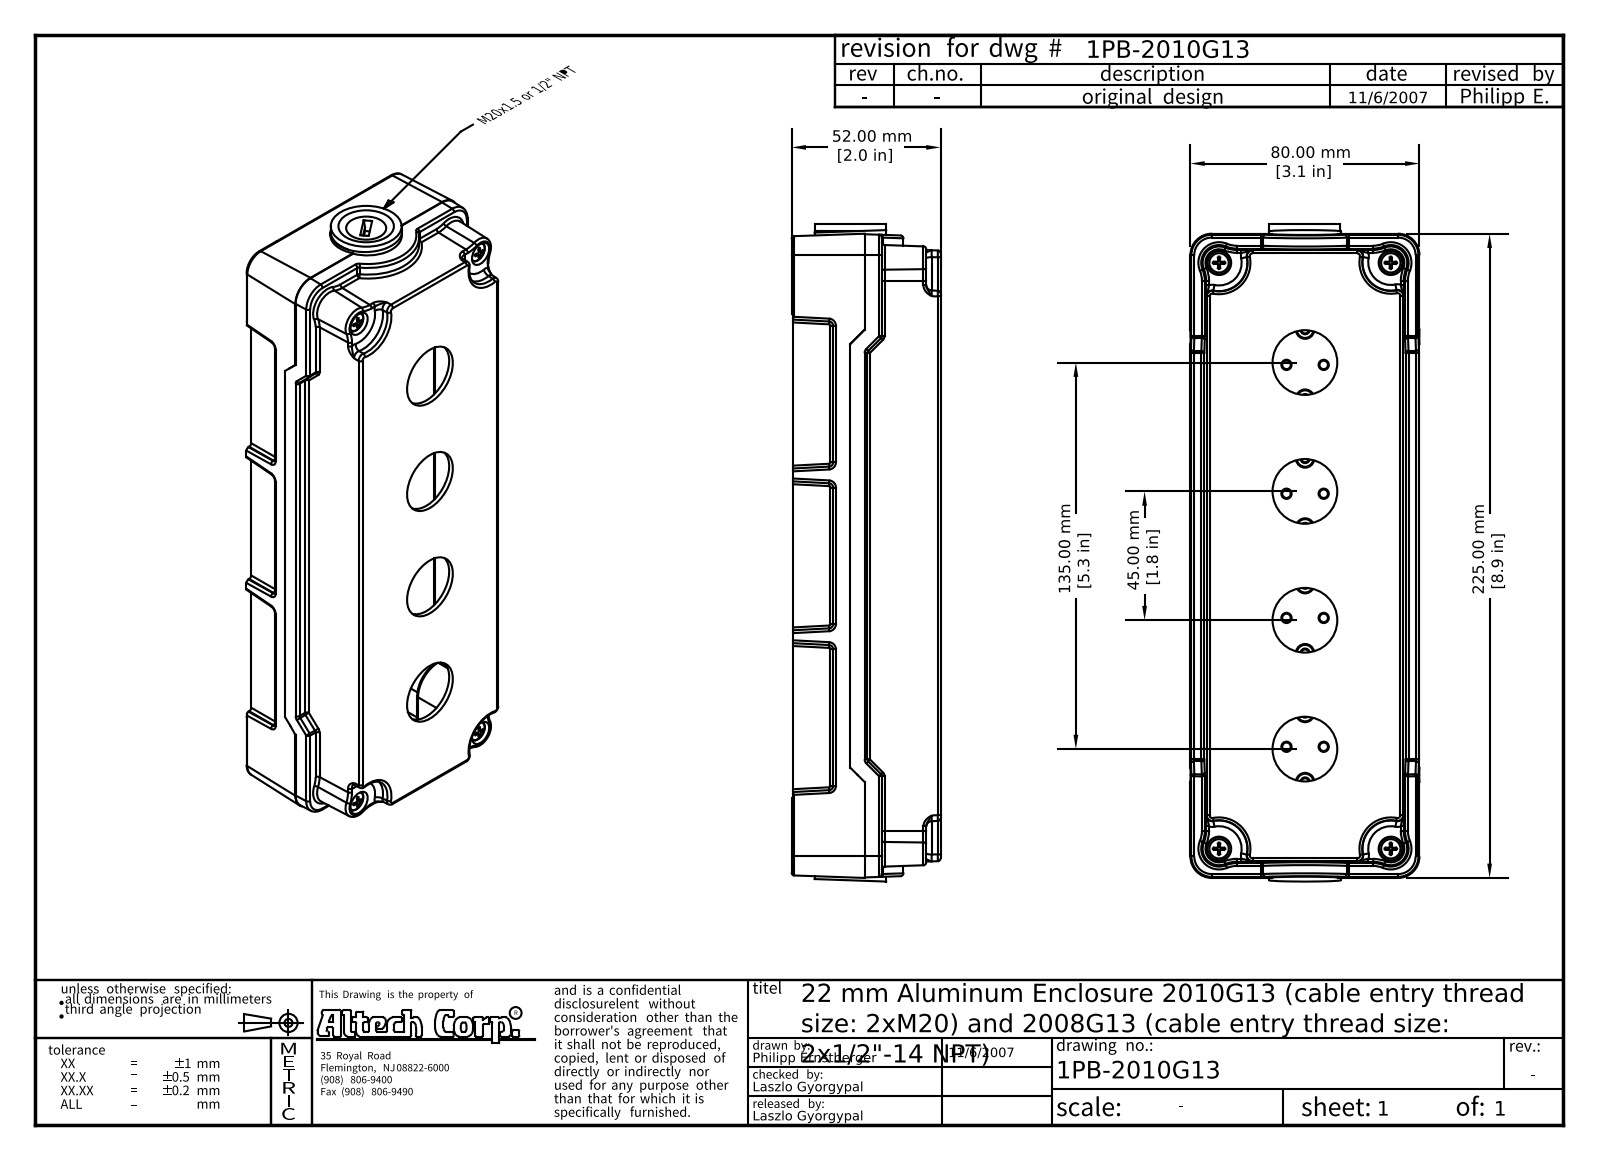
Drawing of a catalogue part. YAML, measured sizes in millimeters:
part_name: "2010G13; enclosure_back; enclosure_front; DIN EN ISO 1207 M3 x 8 (+3 more)"
step_written_by: "Autodesk Inventor 2008 (AUTOMOTIVE_DESIGN)"
units: millimeters
bodies: {solids: 10, faces: 1258, planar: 377, cylindrical: 307, other: 574}
overall_size: [229.6, 80, 52]
volume: 179211
surface_area: 147239
round_holes:
  - {diameter: 3.75, count: 4}
  - {diameter: 9, count: 4}
  - {diameter: 22.6, count: 4}
  - {diameter: 4.5, count: 2}
  - {diameter: 18.7, count: 1}
  - {diameter: 25, count: 1}
round_bosses_or_shafts:
  - {diameter: 8, count: 4}
  - {diameter: 4, count: 4}
  - {diameter: 4.1, count: 2}
  - {diameter: 3, count: 2}
  - {diameter: 2.69, count: 2}
  - {diameter: 24.75, count: 1}
partial_cylinders:
  - {radius: 1, count: 88}
  - {radius: 0.9, count: 16}
  - {radius: 1.75, count: 14}
  - {radius: 1.5, count: 12}
  - {radius: 4.6, count: 12}
  - {radius: 8.1, count: 12}
  - {radius: 2.83, count: 8}
  - {radius: 4.64, count: 7}
face_to_face_distances: [1.8, 49.7, 51.5, 47.9, 1.81, 68.06, 66.25, 69.87, 26.5, 13.5]
hole_center_spacings: [45, 60, 203.85, 9.82, 9.83, 39.05, 45.96, 45.97]
